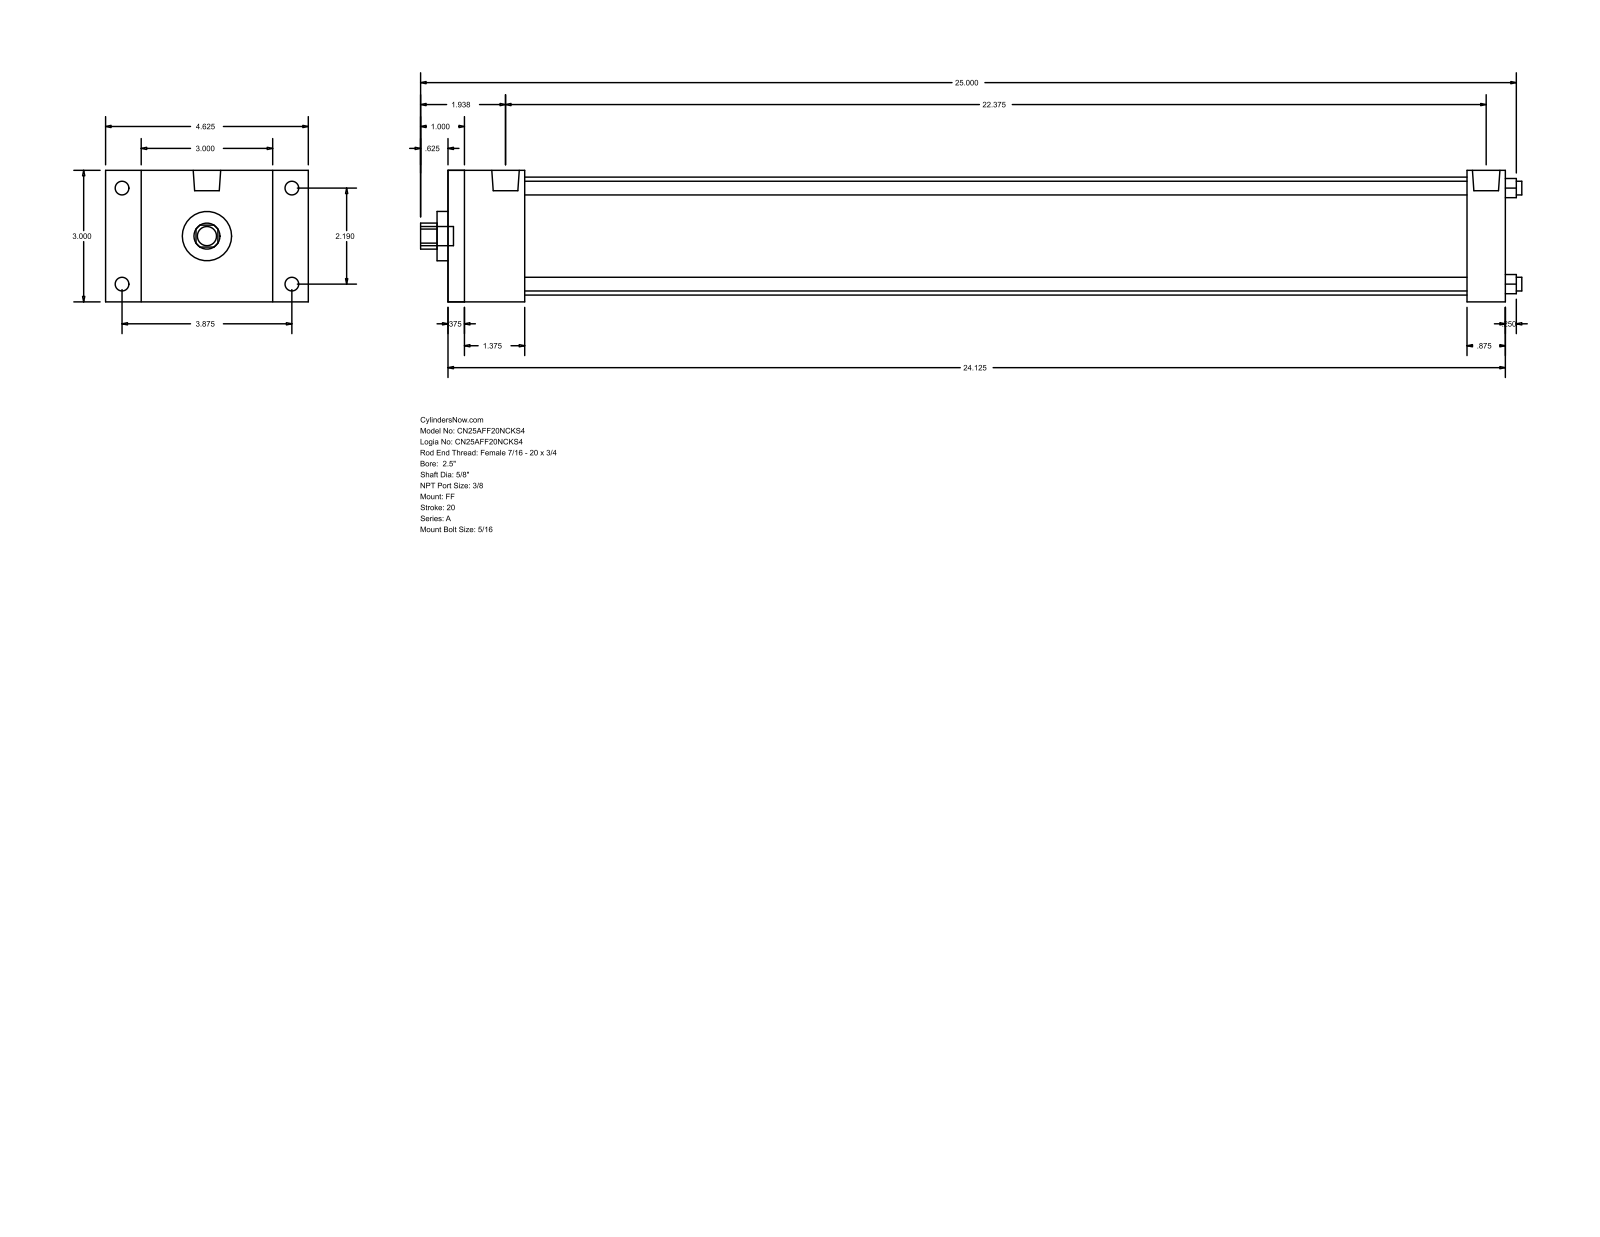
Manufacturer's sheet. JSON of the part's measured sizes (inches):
{"part_name": "A_FF__0250_0.625", "step_written_by": "GSSL Pune (CONFIG_CONTROL_DESIGN)", "units": "inches", "bodies": {"solids": 0, "faces": 92, "planar": 64, "cylindrical": 28, "other": 0}, "overall_size": [25.125, 4.625, 3], "round_holes": [[0.313, 4], [0.625, 1], [1.125, 1], [2.69, 1]], "round_bosses_or_shafts": [[0.313, 4], [0.219, 4], [0.627, 2], [0.437, 1]], "partial_cylinders_radius": [[0.297, 1]], "face_to_face_distances": [3, 24.125, 0.375, 23.75, 1.75, 23.25, 1.375, 22.875, 21.5, 22.375], "hole_center_spacings": [1.548, 2.19, 3.097]}
